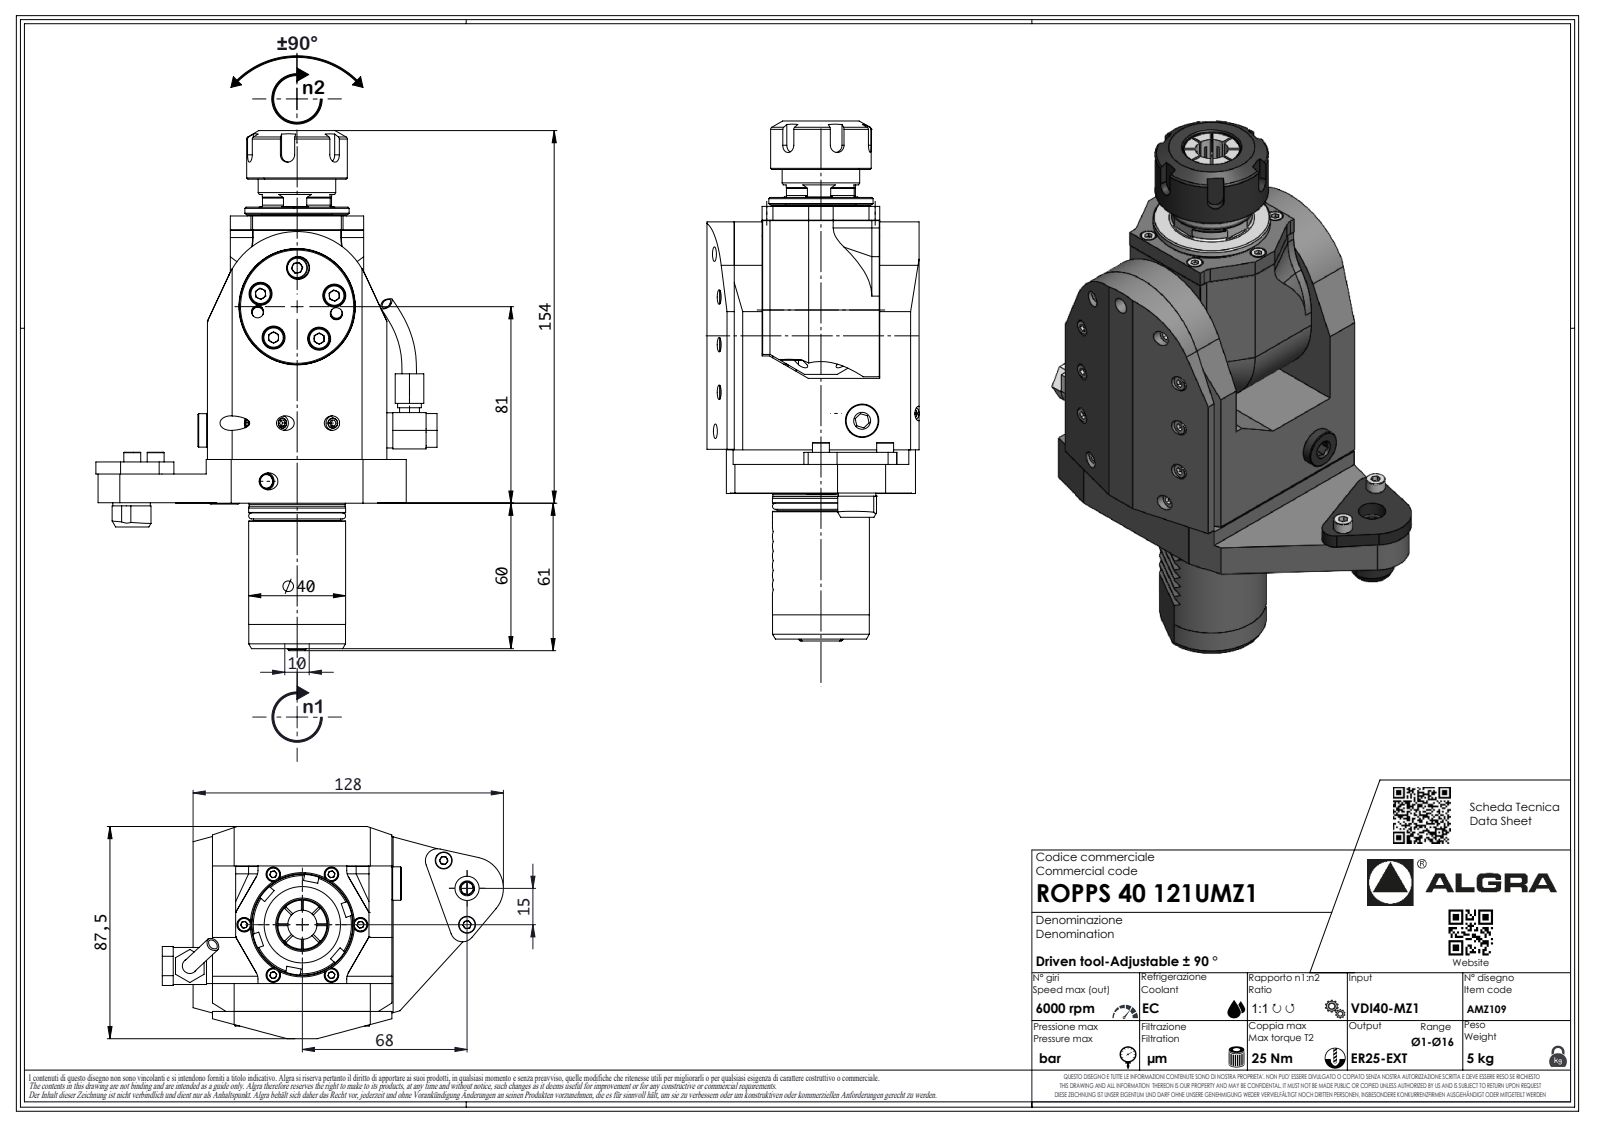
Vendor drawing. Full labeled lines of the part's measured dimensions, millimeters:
Part name (STEP PRODUCT): ROPPS40121UMZ1
STEP written by: SolidWorks 2023 (AUTOMOTIVE_DESIGN)
Units: millimetres
Bodies: 1 solid, 621 faces (416 planar, 97 cylindrical, 108 other)
Overall size (bounding box): 214.39 × 140.7 × 87.5
Volume: 738 734 mm³ · Surface area: 78 658 mm²
Round holes (diameter × count): ⌀2.1 ×1
Round bosses / shafts (diameter × count): ⌀7 ×2, ⌀43 ×1, ⌀41.5 ×1, ⌀41 ×1, ⌀40 ×1, ⌀39.9 ×1, ⌀39.6 ×1, ⌀36 ×1
Partial cylindrical surfaces — rounded edges, fillets, slot ends (radius × count): R0.33 ×7, R0.52 ×7, R1.75 ×7, R3.7 ×7, R3 ×6, R5.1 ×4, R5 ×2, R20 ×2
Main face-to-face distances: 74, 8, 47.5, 14.75, 63.25, 78, 64.75, 55, 60, 118.4
